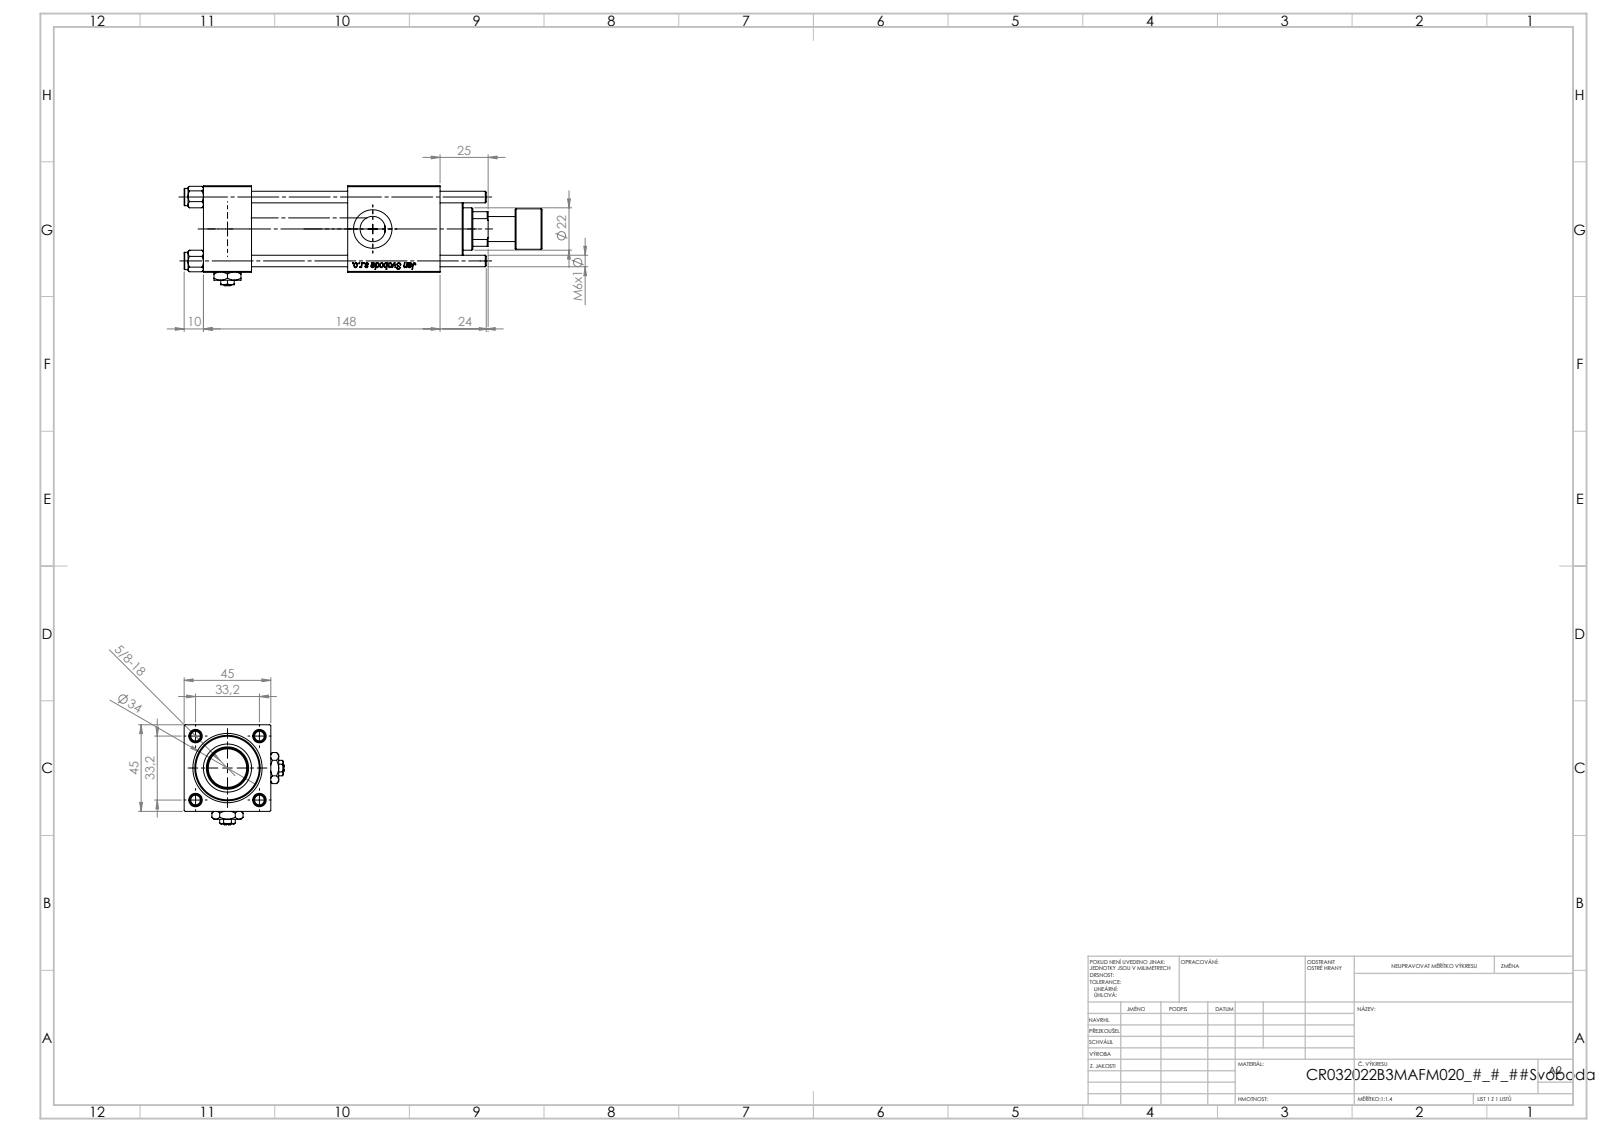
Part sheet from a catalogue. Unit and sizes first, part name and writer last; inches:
Units: inches
Overall size (bounding box): 7.323 × 2.047 × 2.047
Round holes (diameter × count): ⌀0.236 ×4, ⌀0.276 ×2, ⌀0.518 ×2, ⌀0.787 ×2, ⌀0.413 ×1, ⌀0.512 ×1, ⌀0.866 ×1, ⌀0.945 ×1, ⌀0.984 ×1, ⌀1.26 ×1, ⌀1.299 ×1
Round bosses / shafts (diameter × count): ⌀0.354 ×4, ⌀1.496 ×1, ⌀1.339 ×1, ⌀0.827 ×1, ⌀0.512 ×1
Main face-to-face distances: 1.772, 0.984, 4.843, 1.969, 2.953, 3.858, 1.89, 1.764, 3.713, 2.728
Hole centre spacings: 0.924, 1.307, 1.848
Volume: 13.37 in³ · Surface area: 125.3 in²
Bodies: 14 solids, 1267 faces (479 planar, 94 cylindrical, 694 other)
Part name (STEP PRODUCT): V215CR_ROD_END_F; Zatka_pro_OIL_PORT; V215CR_B-1; V215CR_B_TYCINKA (+3 more)
STEP written by: SolidWorks 2019 (CONFIG_CONTROL_DESIGN)
